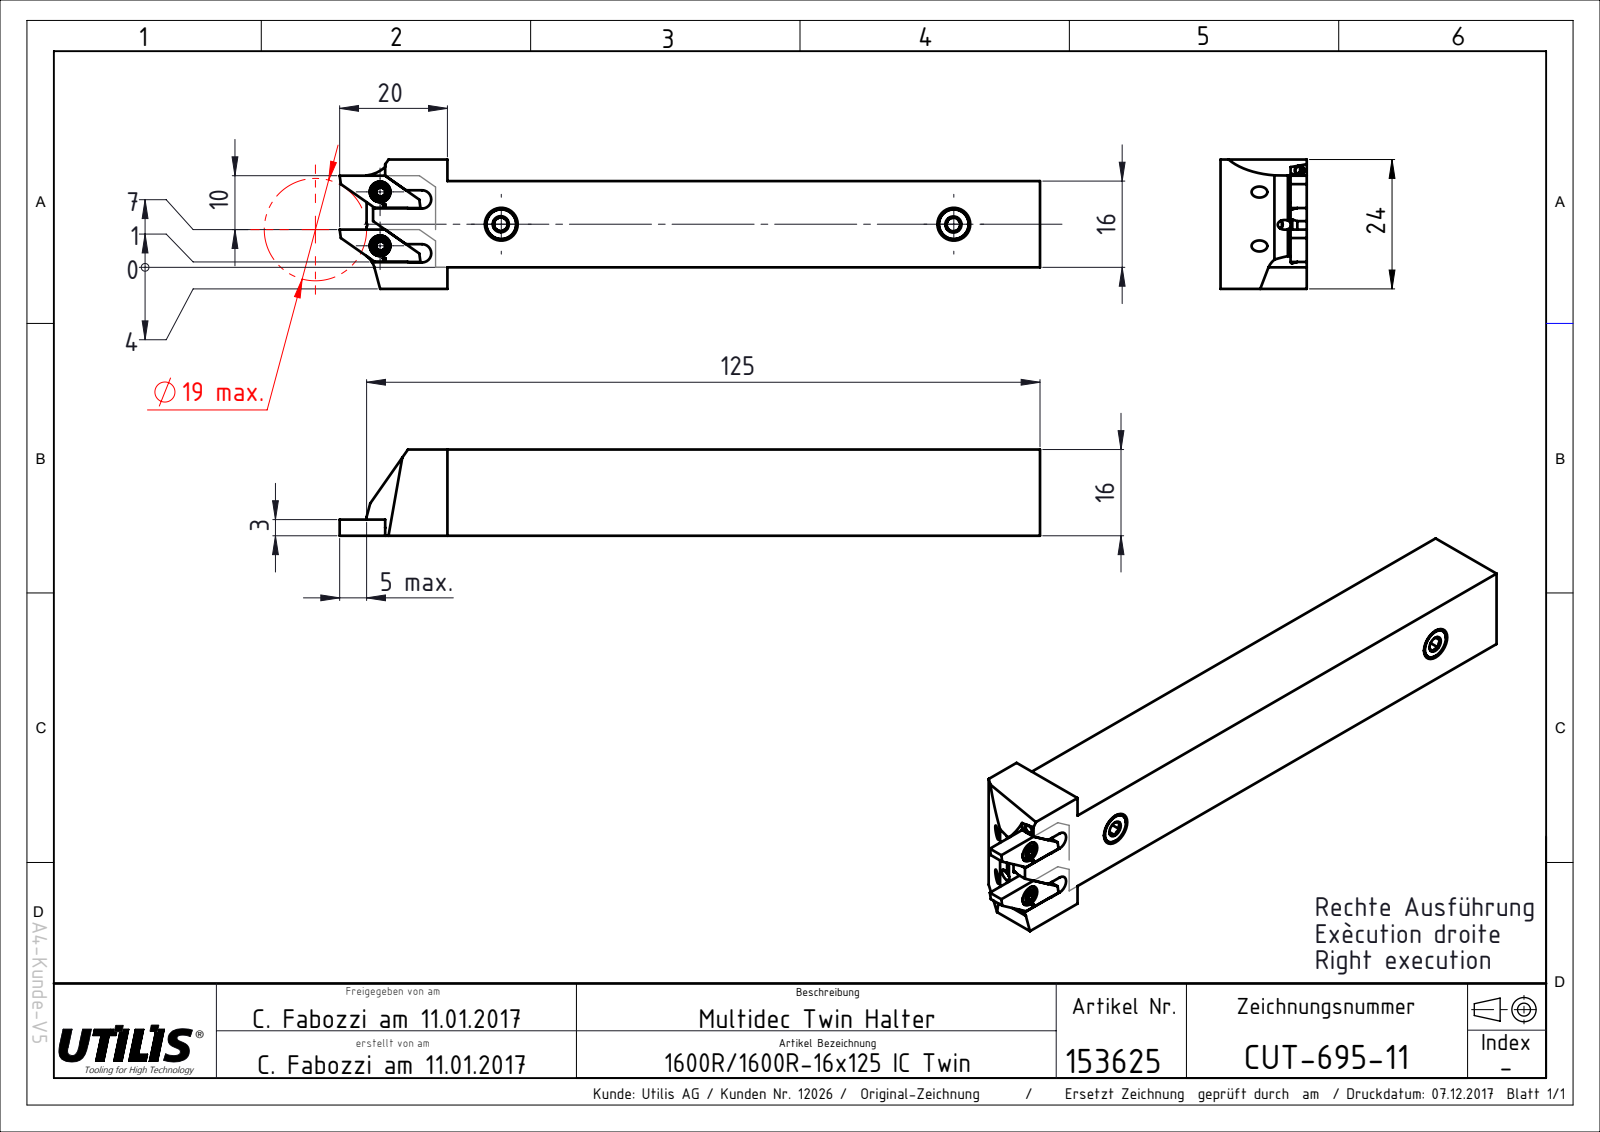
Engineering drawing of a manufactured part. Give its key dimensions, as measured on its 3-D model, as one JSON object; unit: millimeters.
{"part_name": "CUT-695-11", "step_written_by": "SolidWorks 2016 (AUTOMOTIVE_DESIGN)", "units": "millimeters", "bodies": {"solids": 1, "faces": 88, "planar": 79, "cylindrical": 9, "other": 0}, "overall_size": [130, 24, 16], "volume_mm3": 32764, "surface_area_mm2": 8972, "partial_cylinders_radius": [[0.5, 2], [1.55, 2], [1.7, 2], [4.1, 1]], "face_to_face_distances": [16, 4, 20, 110, 24, 13, 3, 6, 10, 15]}
